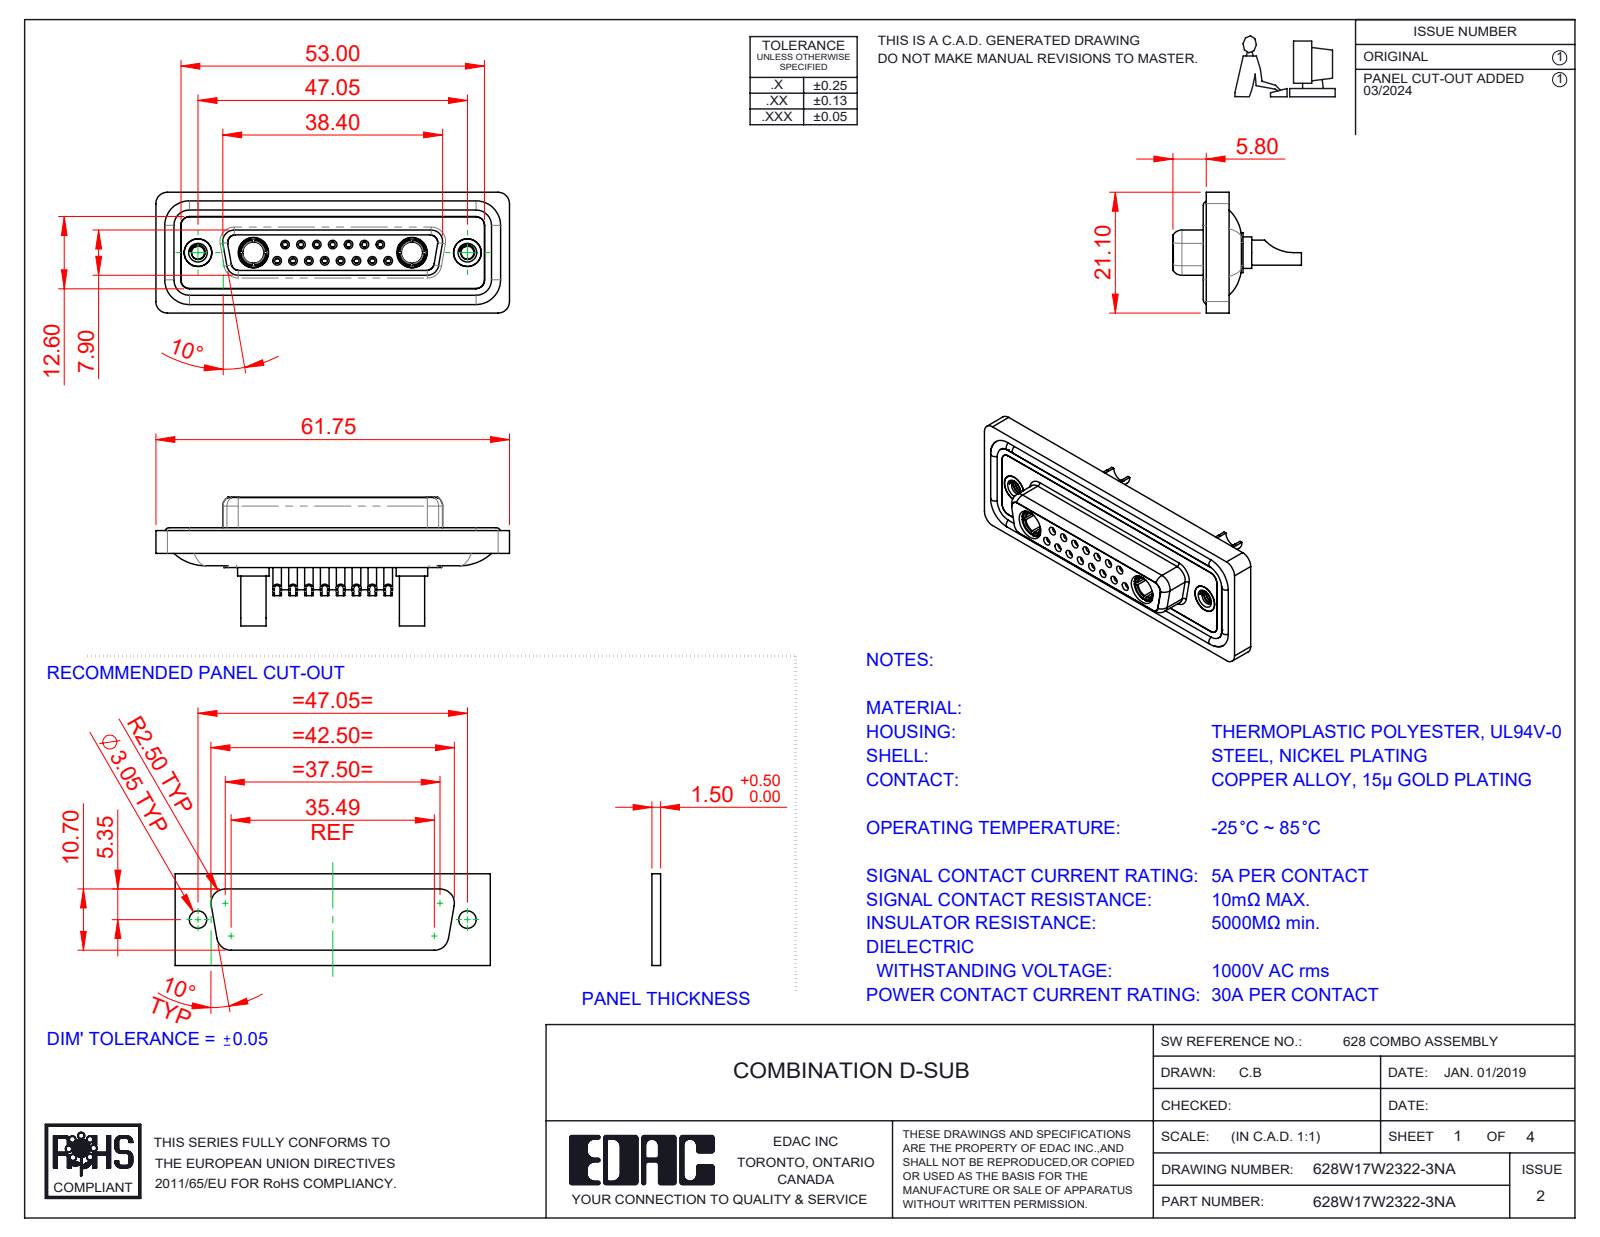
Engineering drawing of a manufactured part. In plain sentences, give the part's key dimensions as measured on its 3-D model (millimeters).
The part is named "628Combo Contact Row 2_22; 628Combo Shell Rear_25 Contacts; 628Combo Contact Row 1_22; 628Combo Waterproof Housing_25 Contacts (+5 more)". Its 3-D file was written by "SolidWorks 2023 (CONFIG_CONTROL_DESIGN)". It is 26 solids with 1369 faces: 424 planar, 557 cylindrical and 388 other. Overall it measures 61.75 by 22.45 by 21.1 millimeters. Its volume is 8 405 cubic millimeters and its surface area 14 228 square millimeters. Round holes: 15 of diameter 0.9, 15 of diameter 1, 15 of diameter 1.1, 15 of diameter 1.5, 15 of diameter 2, 8 of diameter 1.6, 7 of diameter 1.7, 4 of diameter 4.85, 2 of diameter 2.26, 2 of diameter 3.5, 2 of diameter 3.7, 2 of diameter 4. Round bosses or shafts: 15 of diameter 2.2, 11 of diameter 1.6, 2 of diameter 5.5, 2 of diameter 5.2, 2 of diameter 4.96, 2 of diameter 4.95, 2 of diameter 4.8, 2 of diameter 4.75. Partial cylindrical surfaces (rounded edges, fillets, slot ends): 22 of radius 1.5, 18 of radius 2, 8 of radius 1.35, 8 of radius 1.6, 6 of radius 1, 4 of radius 0.25, 4 of radius 0.5, 4 of radius 0.6. The main face-to-face distances are 0.4, 1.8, 7.45, 5.65, 6.6, 0.5, 7.05, 1.6, 2.9, 1.1. The hole center spacings are 3.16, 2.77, 8.31, 5.54, 5.03, 5.04, 7.49, 11.08.
